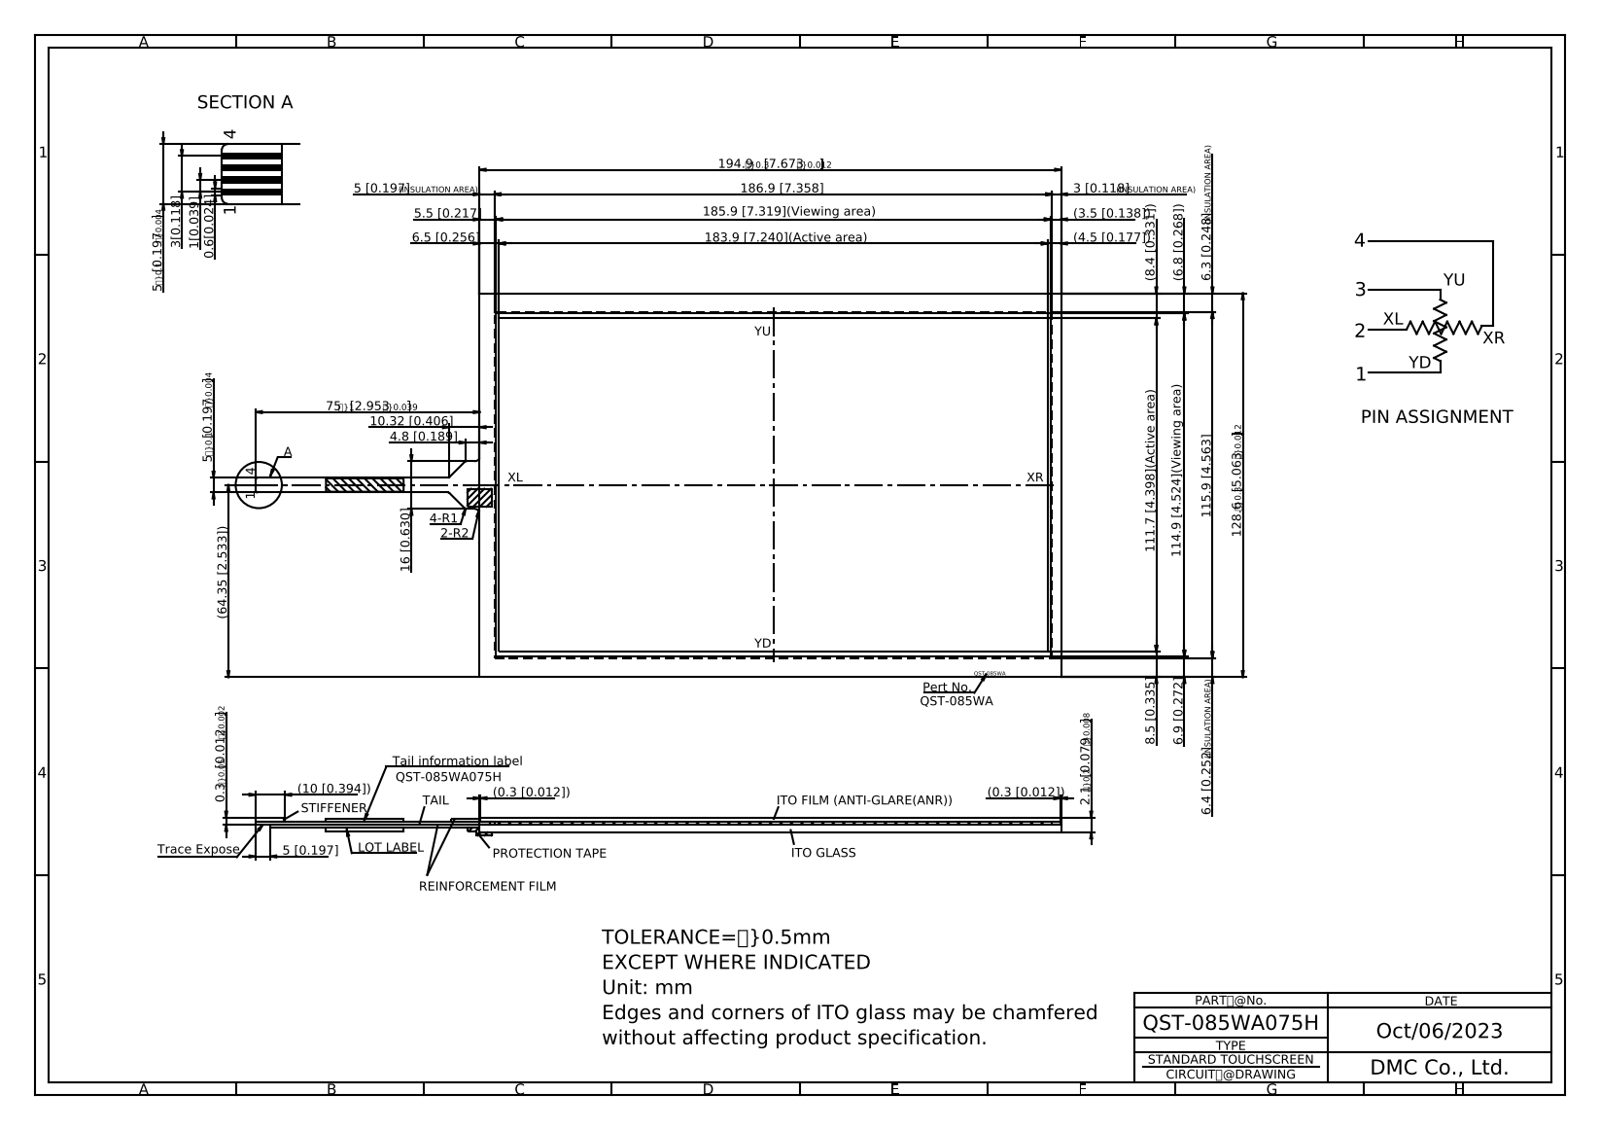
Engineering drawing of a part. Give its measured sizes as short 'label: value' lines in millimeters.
name: QST-085WA075H
written by: Autodesk Inventor 2020 (CONFIG_CONTROL_DESIGN)
unit: mm
bodies: 1 solid, 51 faces (45 planar, 6 cylindrical, 0 other)
size: 308.88 × 180.04 × 2.2
volume: 52 611 mm³; area: 52 540 mm²
rounds: 2× R0.5, 2× R1, 2× R2
face distances: 2.1, 2, 1.8, 1.9, 128.6, 194.9, 0.4, 2.2, 1.6, 113.3
